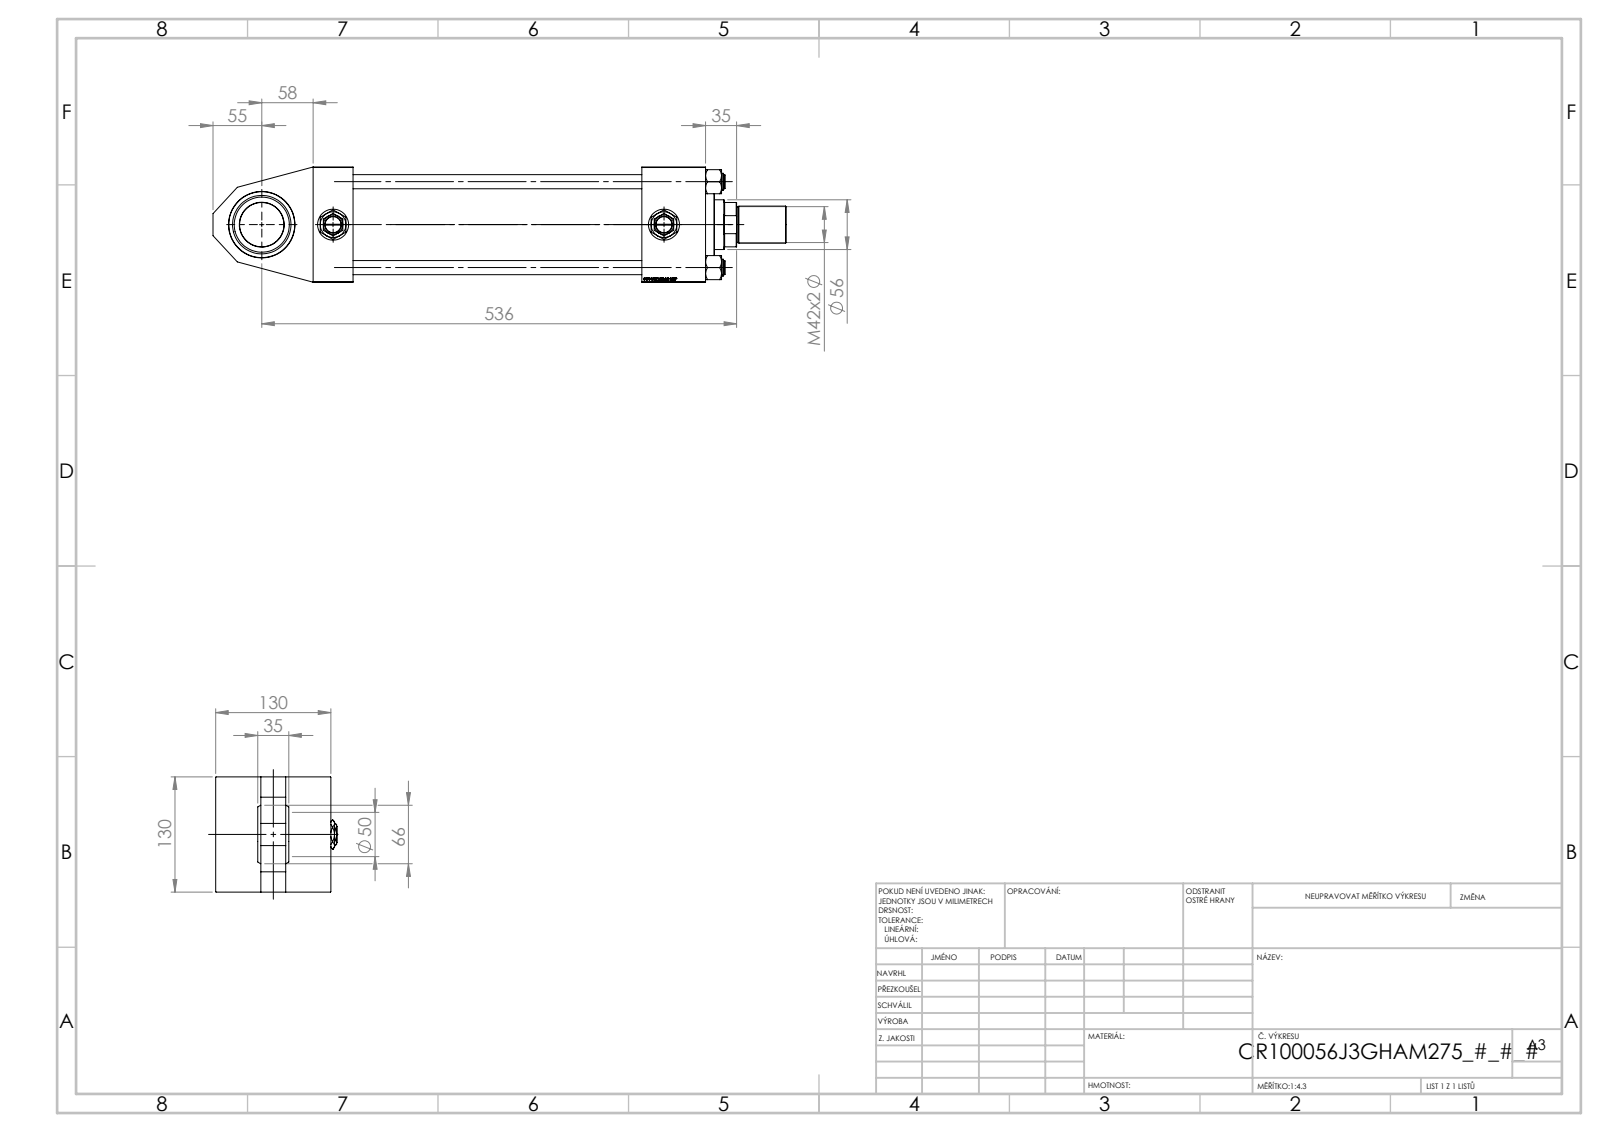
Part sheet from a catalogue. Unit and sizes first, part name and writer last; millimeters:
Units: millimetres
Overall size (bounding box): 647 × 137 × 130
Round holes (diameter × count): ⌀16 ×4, ⌀2.5 ×2, ⌀7 ×2, ⌀26.44 ×2, ⌀35 ×2, ⌀40.5 ×1, ⌀50 ×1, ⌀56 ×1, ⌀59 ×1, ⌀75 ×1, ⌀76 ×1, ⌀85.5 ×1
Round bosses / shafts (diameter × count): ⌀19 ×4, ⌀106 ×1, ⌀72 ×1, ⌀42 ×1, ⌀40 ×1
Partial cylindrical surfaces — rounded edges, fillets, slot ends (radius × count): R27 ×1
Main face-to-face distances: 130, 51, 79, 45, 443, 398, 371, 326, 72, 28
Hole centre spacings: 49.02, 68.52, 96.9, 101.73, 41, 137.04, 80.5, 82
Volume: 3 892 000 mm³ · Surface area: 657 782 mm²
Bodies: 15 solids, 1308 faces (616 planar, 104 cylindrical, 588 other)
Part name (STEP PRODUCT): NUT_M5_J; V215CR_VCP_J; V215_VC_A; V215CR_J_Body (+4 more)
STEP written by: SolidWorks 2019 (CONFIG_CONTROL_DESIGN)
